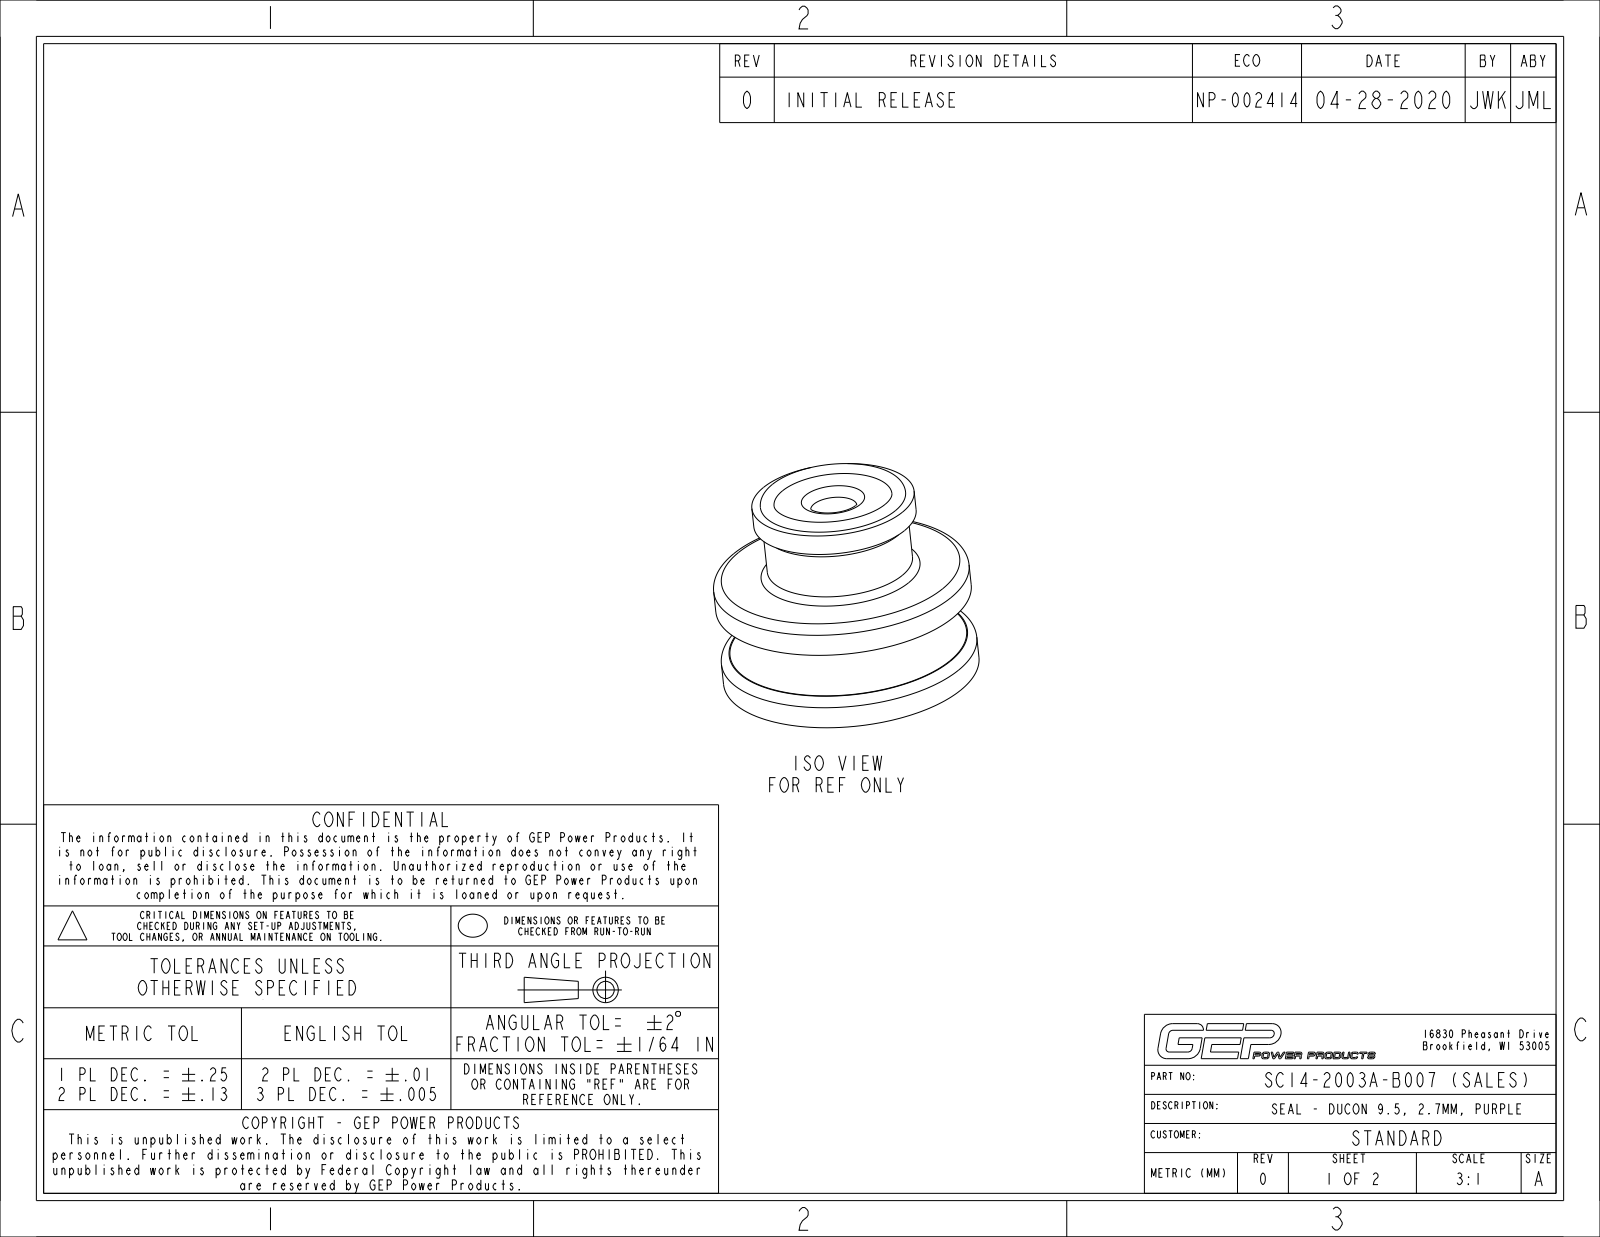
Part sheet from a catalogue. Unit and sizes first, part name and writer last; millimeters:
Units: millimetres
Overall size (bounding box): 14.95 × 14.95 × 12.1
Round holes (diameter × count): ⌀2.7 ×1
Round bosses / shafts (diameter × count): ⌀14.95 ×1, ⌀9.5 ×1, ⌀8.5 ×1
Main face-to-face distances: 6.5, 11.1, 4.6, 1.8, 4.7, 6.4, 9.9, 5.2, 3.4, 1.2
Volume: 1 160 mm³ · Surface area: 994 mm²
Bodies: 1 solid, 88 faces (42 planar, 10 cylindrical, 36 other)
Part name (STEP PRODUCT): PC14-2003A-B007_NCF; SC14-2003A-B007_NCF_ASM
STEP written by: CREO PARAMETRIC BY PTC INC, 2017110 (CONFIG_CONTROL_DESIGN)
